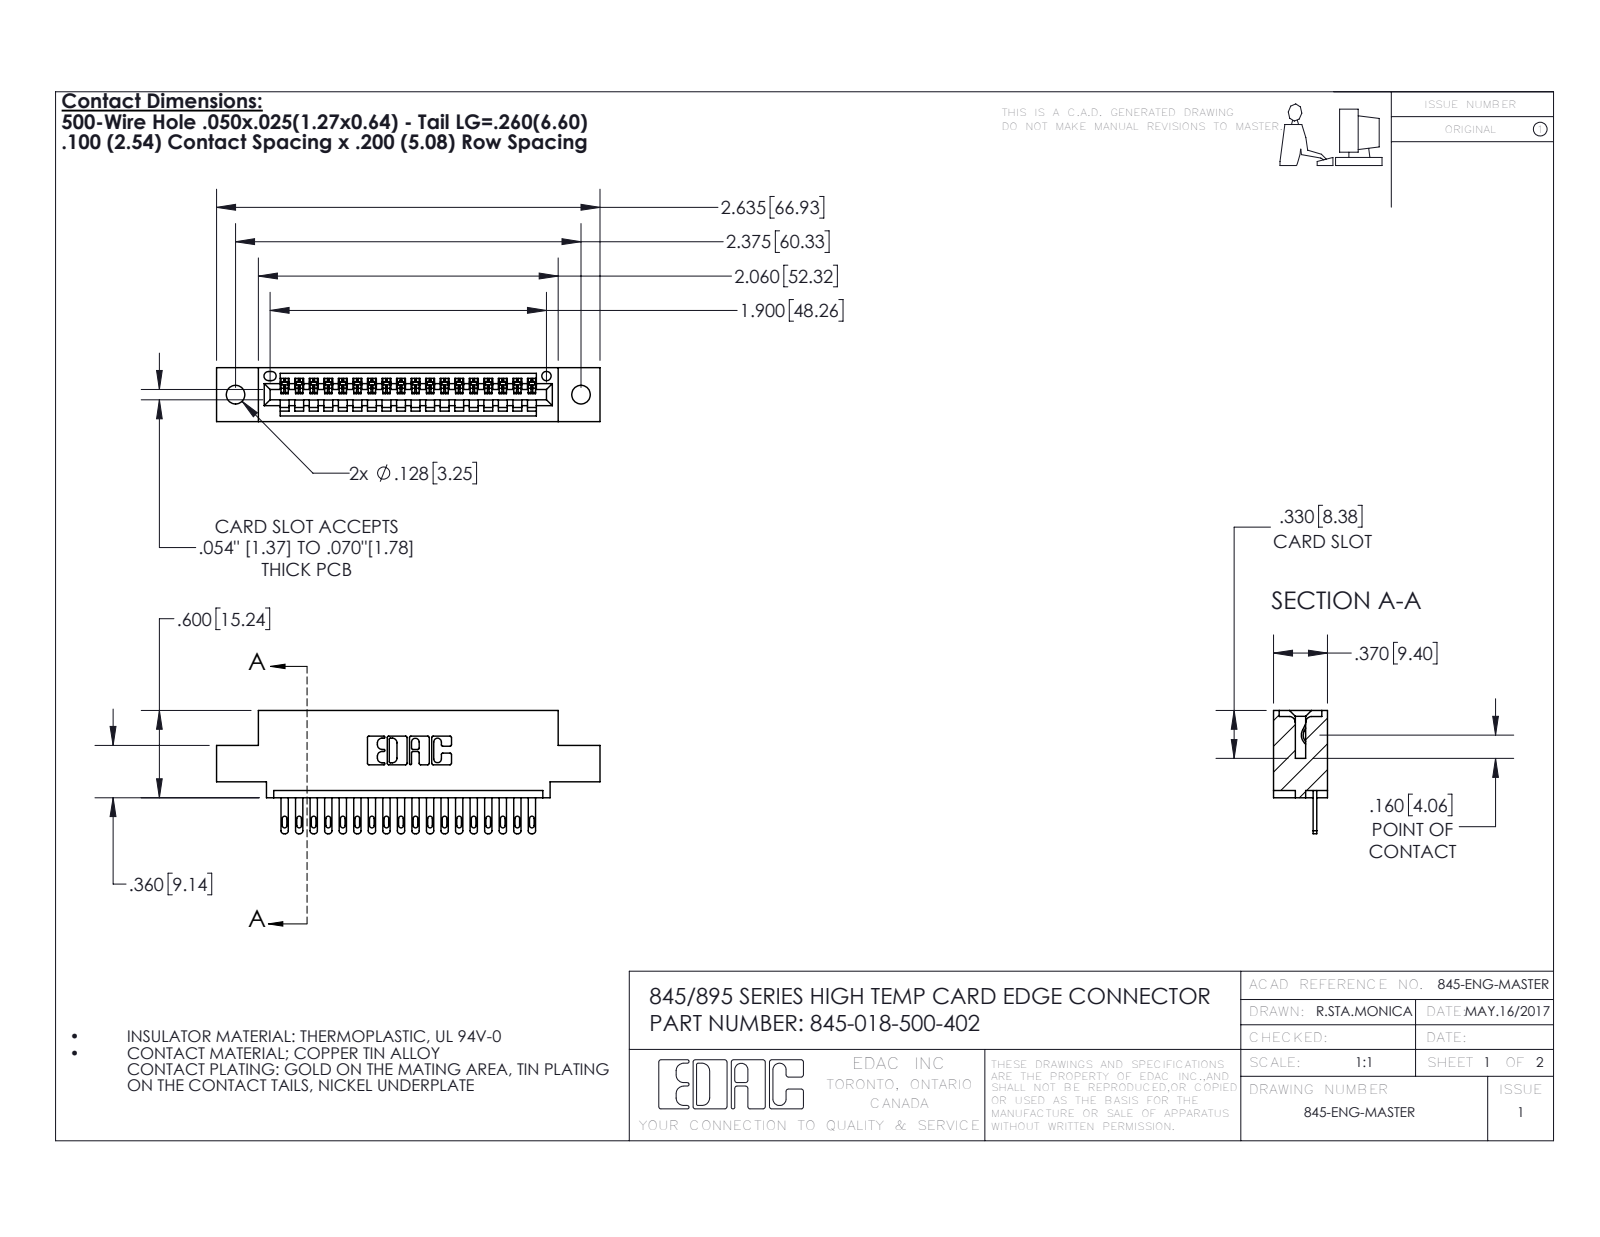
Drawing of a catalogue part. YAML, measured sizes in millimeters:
part_name: "345-018-500-402; 345 Part_0.110 Offset - 0.128 Dia; 345-292-001_345-293-100"
step_written_by: "SolidWorks 2016 (CONFIG_CONTROL_DESIGN)"
units: millimeters
bodies: {solids: 19, faces: 1102, planar: 696, cylindrical: 406, other: 0}
overall_size: [66.9, 21.5, 9.4]
volume: 6060
surface_area: 7581
round_holes:
  - {diameter: 3.3, count: 2}
  - {diameter: 1.6, count: 1}
partial_cylinders:
  - {radius: 0.2, count: 36}
  - {radius: 0.4, count: 36}
  - {radius: 0.5, count: 36}
  - {radius: 0.3, count: 22}
  - {radius: 0.2, count: 6}
  - {radius: 0.8, count: 6}
  - {radius: 0.7, count: 3}
  - {radius: 0.8, count: 2}
face_to_face_distances: [7.6, 1.8, 5.1, 9.4, 2.5, 6.9, 0.6, 5.7, 2.5, 4.1]
hole_center_spacings: [6.9, 54.4, 60.3]
